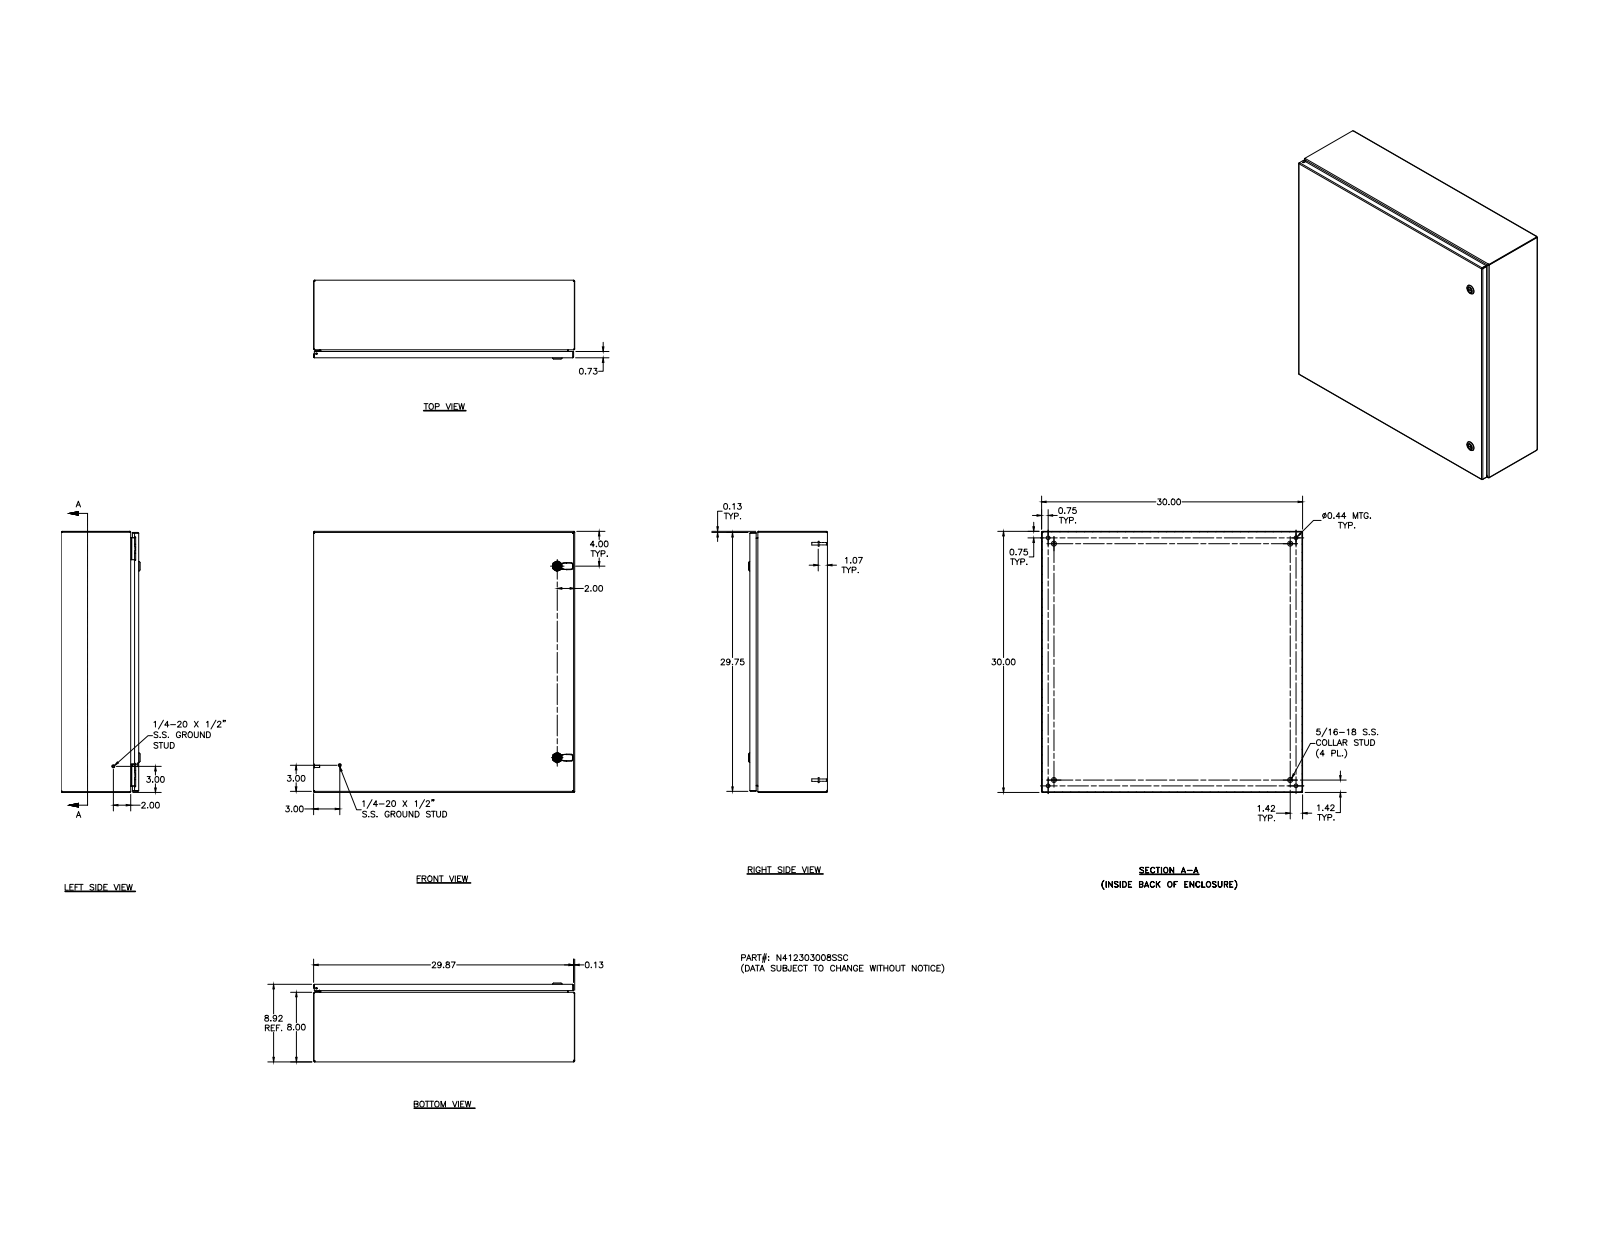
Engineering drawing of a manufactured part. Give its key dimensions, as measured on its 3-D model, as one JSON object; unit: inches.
{"part_name": "N412303008SSC; N412303008SSCBKP; 388151; N4123030SSCLID (+8 more)", "step_written_by": "Autodesk Inventor 2011 (AUTOMOTIVE_DESIGN)", "units": "inches", "bodies": {"solids": 42, "faces": 1682, "planar": 706, "cylindrical": 600, "other": 376}, "overall_size": [30, 30, 9.075], "volume_in3": 222.3, "surface_area_in2": 6028, "round_holes": [[0.188, 5], [0.093, 4], [0.152, 4], [0.167, 4], [0.172, 4], [0.437, 4], [0.156, 2], [0.197, 2], [0.315, 2], [0.394, 2], [0.402, 2], [0.634, 2]], "round_bosses_or_shafts": [[0.25, 10], [0.563, 4], [0.36, 4], [0.32, 4], [0.3, 4], [0.275, 4], [0.256, 4], [0.164, 4]], "partial_cylinders_radius": [[0.031, 30], [0.05, 26], [0.105, 20], [0.016, 18], [0.02, 15], [0.125, 14], [0.032, 8], [0.07, 8]], "face_to_face_distances": [0.074, 8.843, 29.926, 8.917, 8.769, 29.852, 30, 7.926, 0.917, 0.739], "hole_center_spacings": [26, 0.017, 0.66, 28.5, 27.698, 0.019, 0.5, 0.648]}
